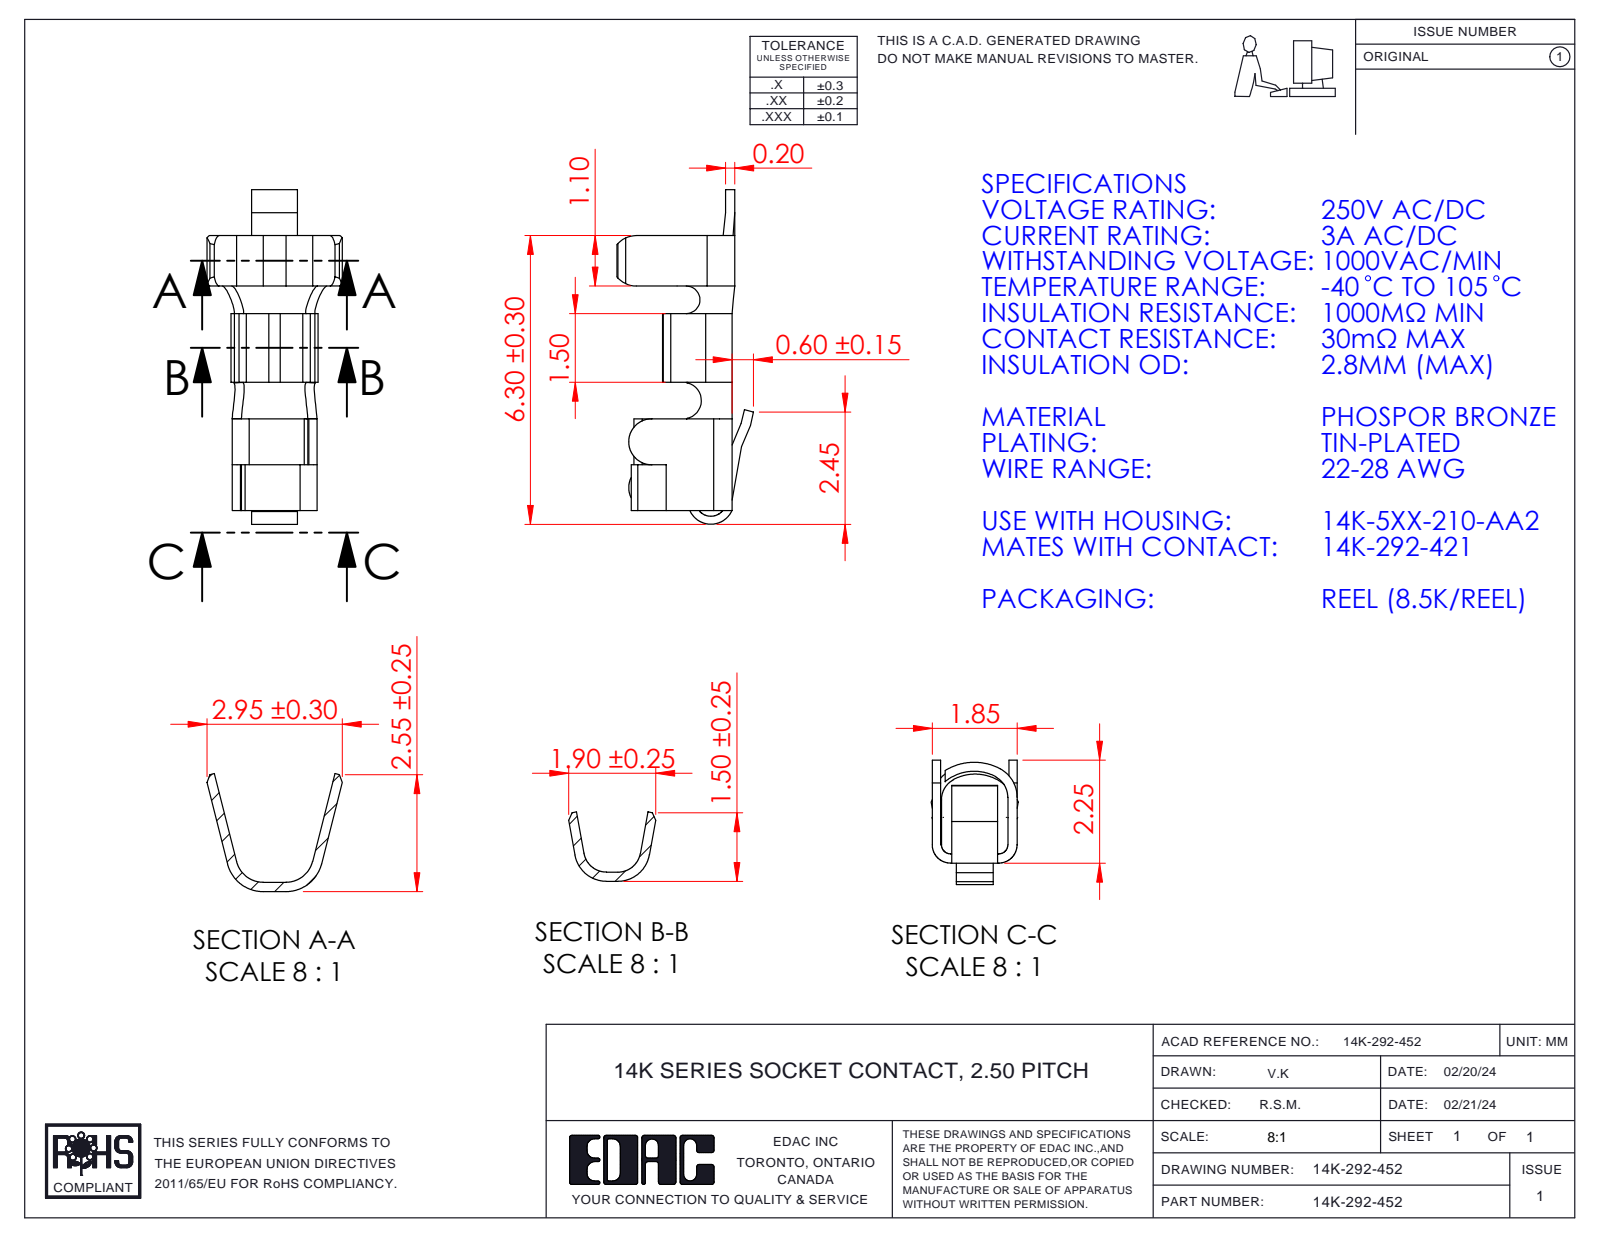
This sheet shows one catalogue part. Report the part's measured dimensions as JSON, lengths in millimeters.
{"part_name": "14K-292-452", "step_written_by": "SolidWorks 2023 (CONFIG_CONTROL_DESIGN)", "units": "millimeters", "bodies": {"solids": 1, "faces": 116, "planar": 69, "cylindrical": 37, "other": 10}, "overall_size": [7.3, 2.98, 2.95], "volume_mm3": 7, "surface_area_mm2": 78, "partial_cylinders_radius": [[0.5, 7], [0.7, 4], [0.4, 3], [0.2, 2], [0.6, 2], [0.8, 2], [1, 2], [1.2, 2]], "face_to_face_distances": [1.86, 1.66, 1, 1.68, 1.67, 1.49, 0.43, 1.43, 1.23, 6]}
